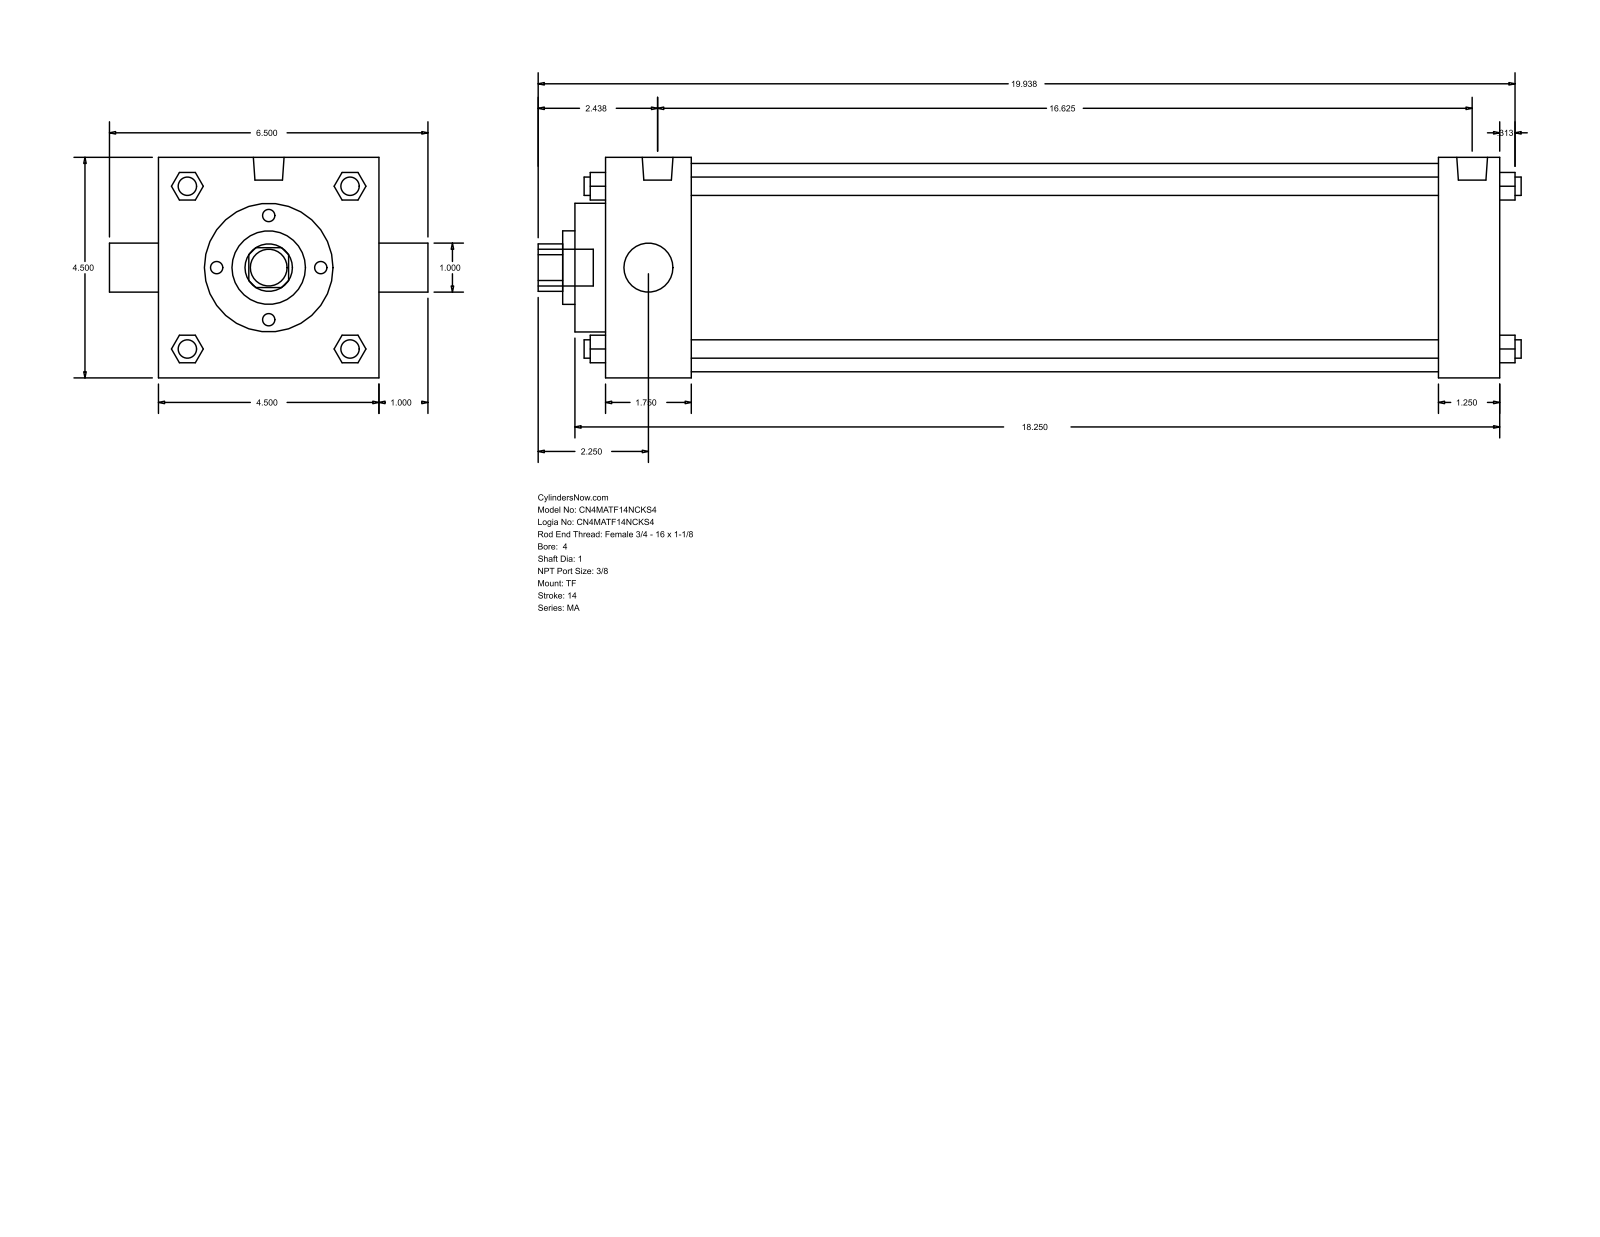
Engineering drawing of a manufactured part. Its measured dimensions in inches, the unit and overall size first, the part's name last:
Units: inches
Overall size (bounding box): 20.063 × 6.5 × 4.5
Round holes (diameter × count): ⌀1 ×2, ⌀1.5 ×1, ⌀2.625 ×1, ⌀4.25 ×1
Round bosses / shafts (diameter × count): ⌀0.375 ×4, ⌀0.437 ×3, ⌀0.627 ×2, ⌀0.75 ×1
Partial cylindrical surfaces — rounded edges, fillets, slot ends (radius × count): R0.484 ×1
Main face-to-face distances: 4.5, 18.25, 17, 1.25, 1.75, 15.25, 16.5, 0.625, 2.375, 17.625
Bodies: 0 solids, 122 faces (93 planar, 29 cylindrical, 0 other)
Part name (STEP PRODUCT): MA_TF__0400_1
STEP written by: GSSL Pune (CONFIG_CONTROL_DESIGN)
